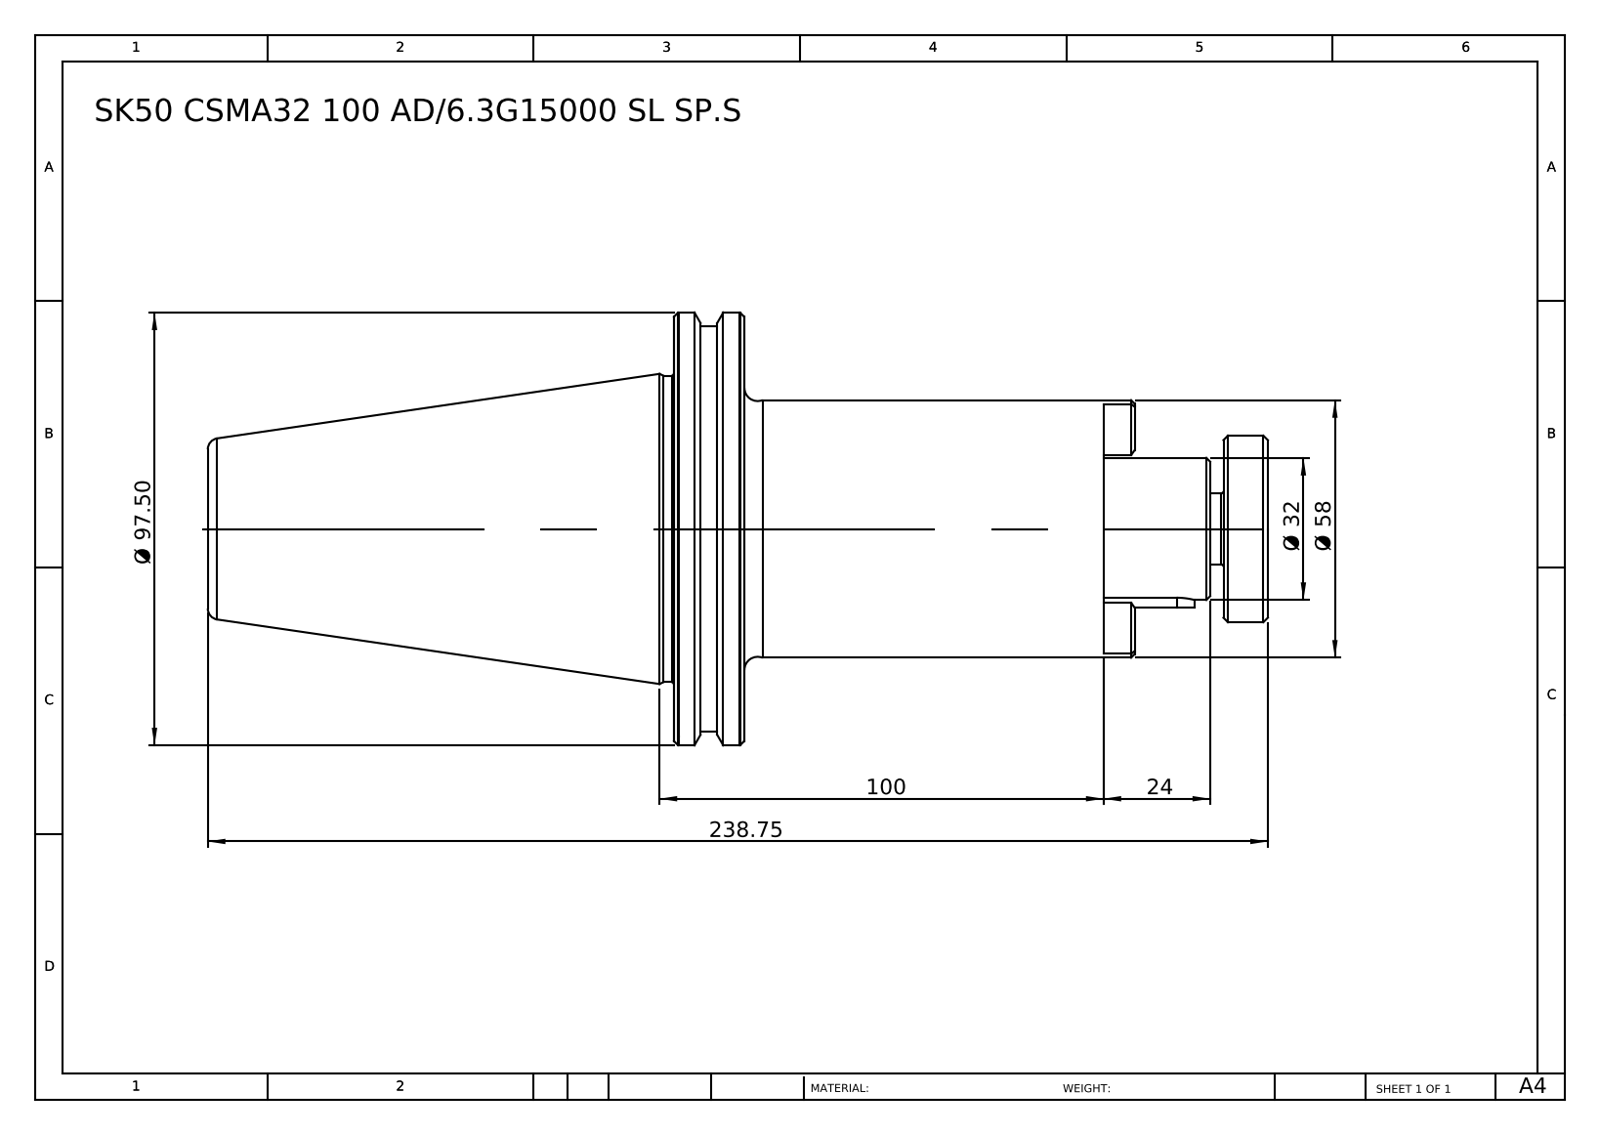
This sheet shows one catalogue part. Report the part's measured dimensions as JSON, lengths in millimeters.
{"part_name": "SK 50 CSMA32 100 AD-6.3G15000 SL SP", "step_written_by": "SolidWorks 2014 (CONFIG_CONTROL_DESIGN)", "units": "millimeters", "bodies": {"solids": 1, "faces": 84, "planar": 23, "cylindrical": 21, "other": 40}, "overall_size": [238.75, 97.5, 97.5], "volume_mm3": 623580, "surface_area_mm2": 57750, "round_bosses_or_shafts": [[97.5, 1], [91.25, 1], [69, 1], [58, 1], [42, 1], [32, 1], [16, 1]], "partial_cylinders_radius": [[4, 1], [18, 1]], "face_to_face_distances": [15.9, 80.9, 96.8, 37, 117.9, 133.8, 10, 27, 107.9, 123.8]}
